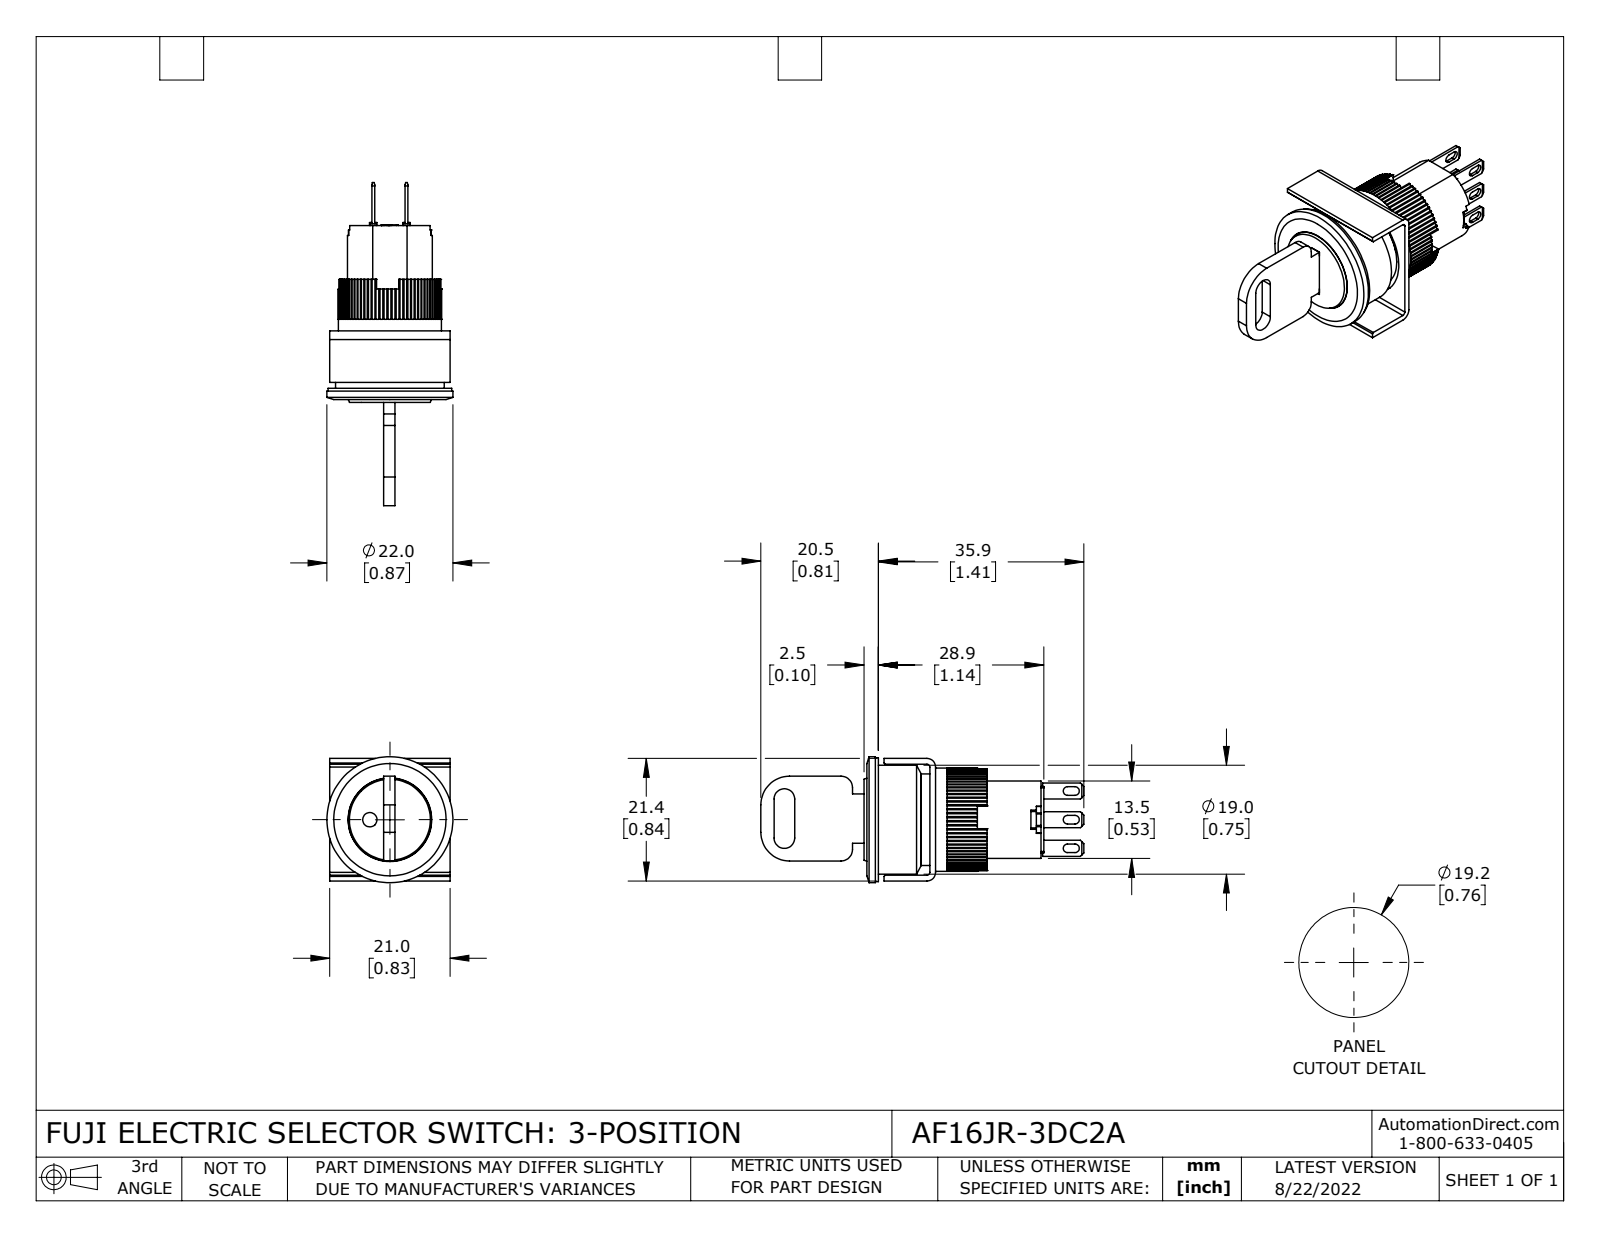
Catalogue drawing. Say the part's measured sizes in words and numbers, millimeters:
The part is named "AF16JR-3DC2A". Its 3-D file was written by "SolidWorks 2021 (CONFIG_CONTROL_DESIGN)". It is 13 solids with 707 faces: 518 planar, 183 cylindrical and 6 other. Overall it measures 56.4 by 22 by 22 millimeters. Its volume is 8 110 cubic millimeters and its surface area 7 252 square millimeters. Round holes: 1 of diameter 1, 1 of diameter 2.5, 1 of diameter 14.6, 1 of diameter 18, 1 of diameter 19. Round bosses or shafts: 1 of diameter 22, 1 of diameter 21.6, 1 of diameter 16, 1 of diameter 14.8, 1 of diameter 14.5. Partial cylindrical surfaces (rounded edges, fillets, slot ends): 80 of radius 0.3, 12 of radius 0.2, 6 of radius 0.8, 2 of radius 0.5, 2 of radius 1.5, 2 of radius 1.8, 2 of radius 2, 2 of radius 5. The main face-to-face distances are 2, 1, 0.5, 9.5, 4.5, 2.5, 10, 20.4, 1.5, 19.4. The hole center spacings are 3.5.
